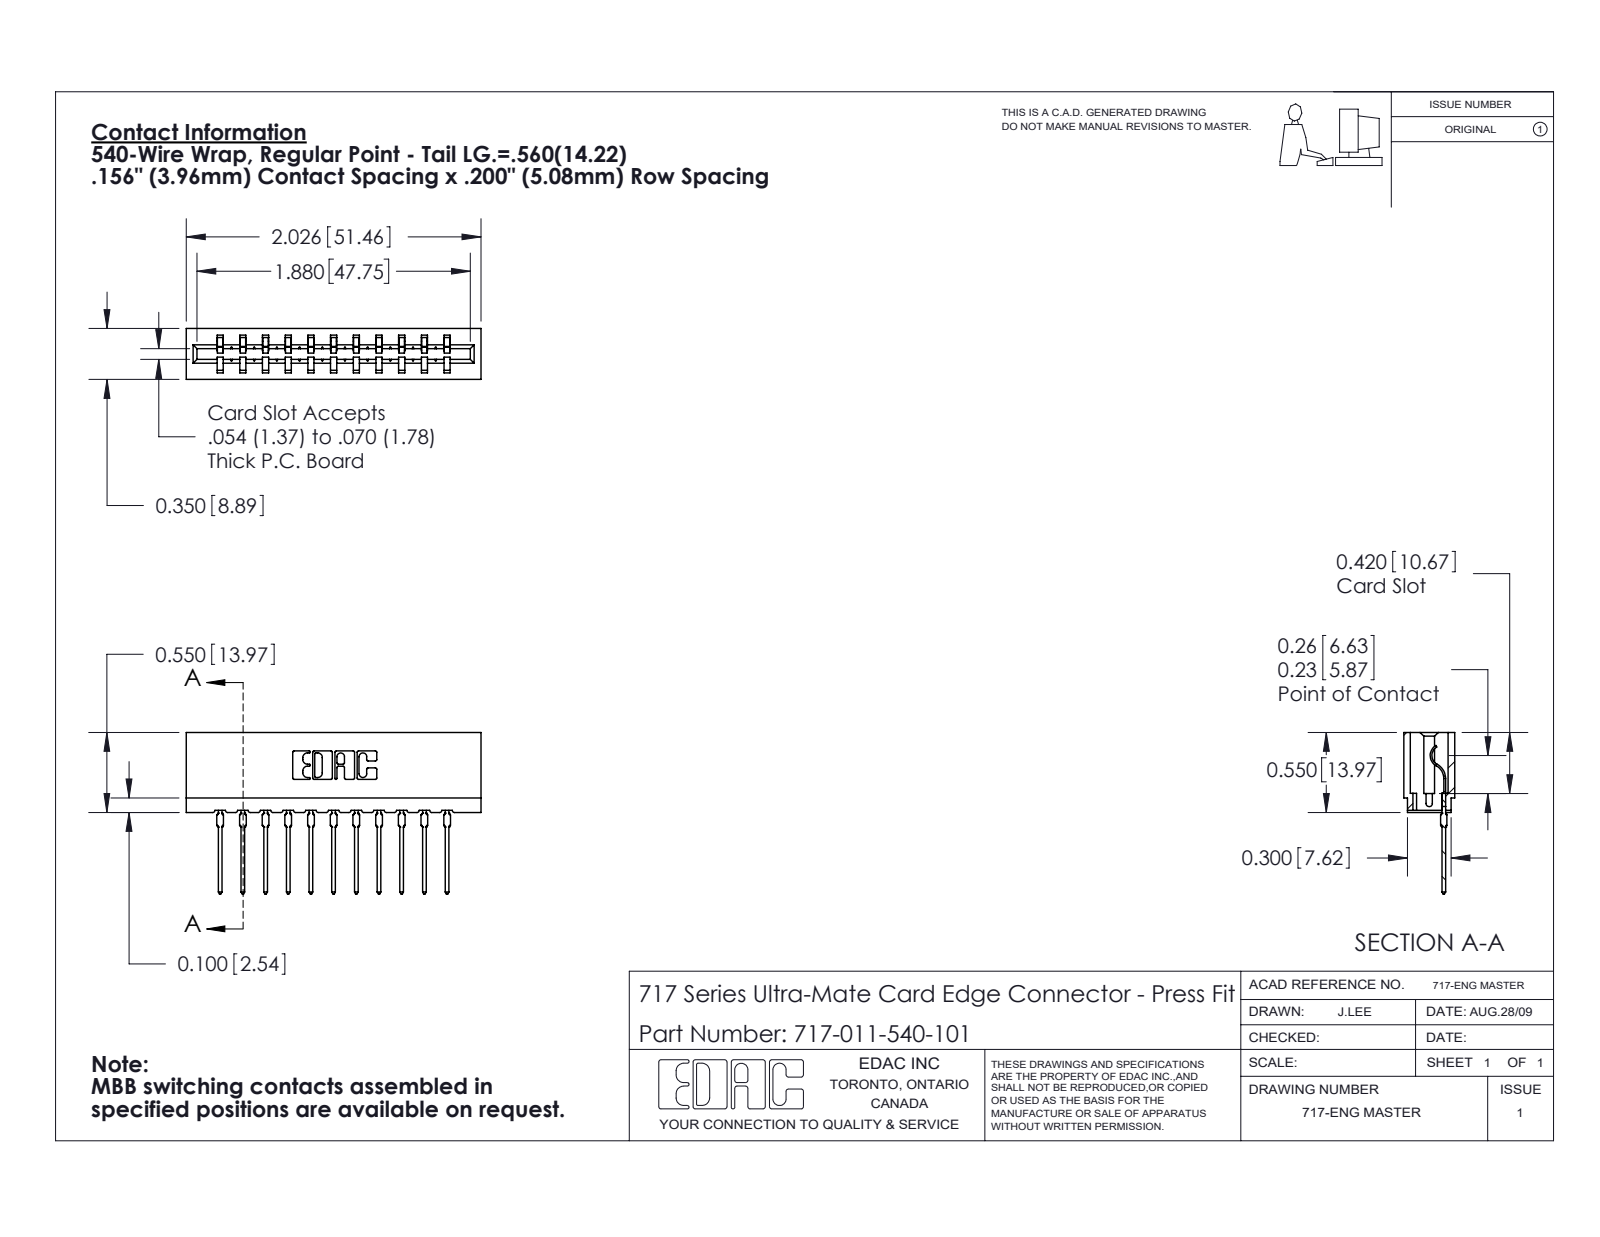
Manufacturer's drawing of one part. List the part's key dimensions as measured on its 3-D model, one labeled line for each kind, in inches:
Part name (STEP PRODUCT): 717-011-540-101; 745-292-001_540; 717 Part_Insulator Option - 06
STEP written by: SolidWorks 2020 (CONFIG_CONTROL_DESIGN)
Units: inches
Bodies: 12 solids, 1337 faces (802 planar, 249 cylindrical, 286 other)
Overall size (bounding box): 2.026 × 1.109 × 0.35
Volume: 0.275 in³ · Surface area: 9.497 in²
Partial cylindrical surfaces — rounded edges, fillets, slot ends (radius × count): R0.01 ×22, R0.015 ×22, R0.021 ×22, R0.007 ×6, R0.031 ×6, R0.005 ×4, R0.011 ×4, R0.026 ×3
Main face-to-face distances: 0.212, 0.156, 0.138, 0.468, 0.624, 0.35, 0.312, 0.198, 0.312, 0.042
